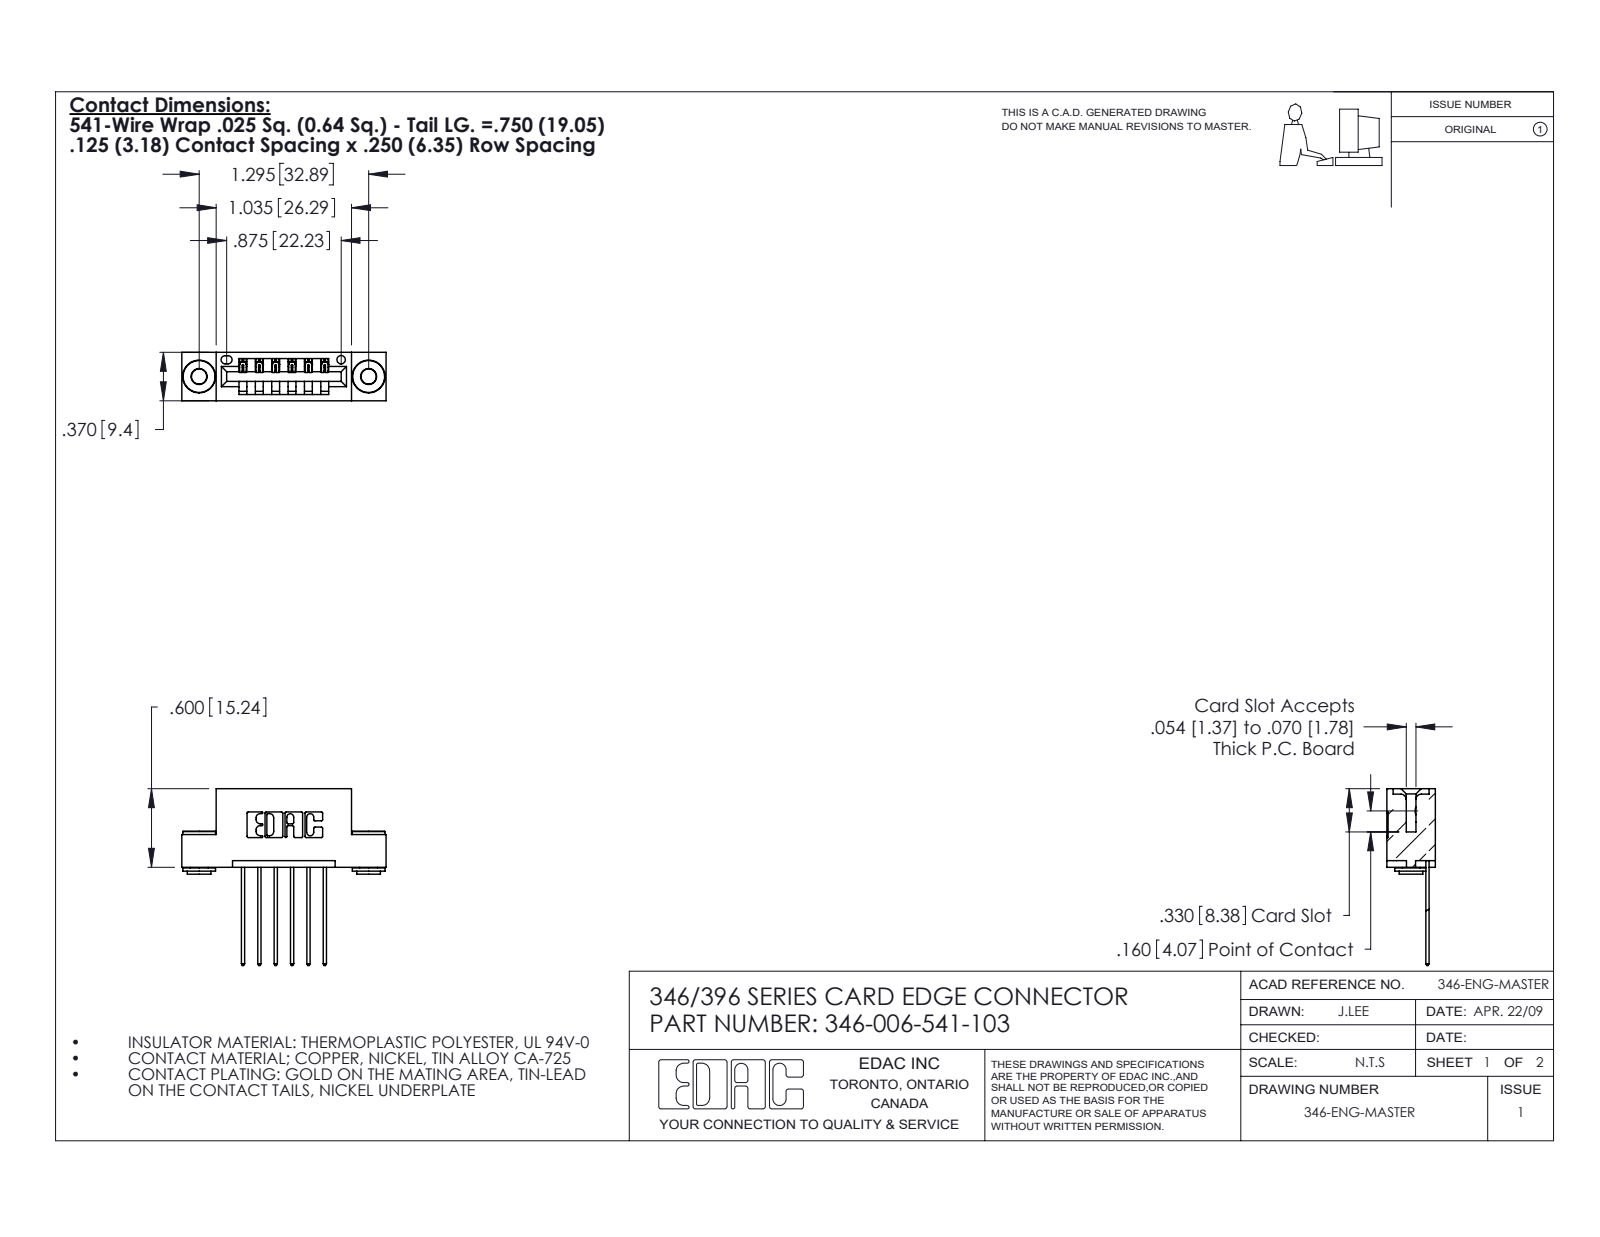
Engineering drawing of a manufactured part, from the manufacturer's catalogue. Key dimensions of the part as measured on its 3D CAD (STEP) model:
Part name (STEP PRODUCT): 345-250-002_345-250-002-102; 345-292-001_345-293-141; 346-006-541-103; 346 Part_Flush Mounting Lugs - 0.156 Dia-TH
STEP written by: SolidWorks 2020 (CONFIG_CONTROL_DESIGN)
Units: inches
Bodies: 9 solids, 522 faces (340 planar, 174 cylindrical, 8 other)
Overall size (bounding box): 1.56 × 1.35 × 0.37
Volume: 0.218 in³ · Surface area: 6.879 in²
Round holes (diameter × count): ⌀0.116 ×2, ⌀0.156 ×2, ⌀0.064 ×1
Round bosses / shafts (diameter × count): ⌀0.25 ×2, ⌀0.18 ×2, ⌀0.136 ×2
Partial cylindrical surfaces — rounded edges, fillets, slot ends (radius × count): R0.01 ×22, R0.006 ×12, R0.01 ×12, R0.007 ×6, R0.031 ×6, R0.026 ×3, R0.031 ×2, R0.04 ×2
Main face-to-face distances: 0.25, 0.37, 0.048, 0.322, 0.025, 0.072, 0.298, 0.148, 0.222, 0.1
Hole centre spacings: 0.246, 1.092, 1.295
